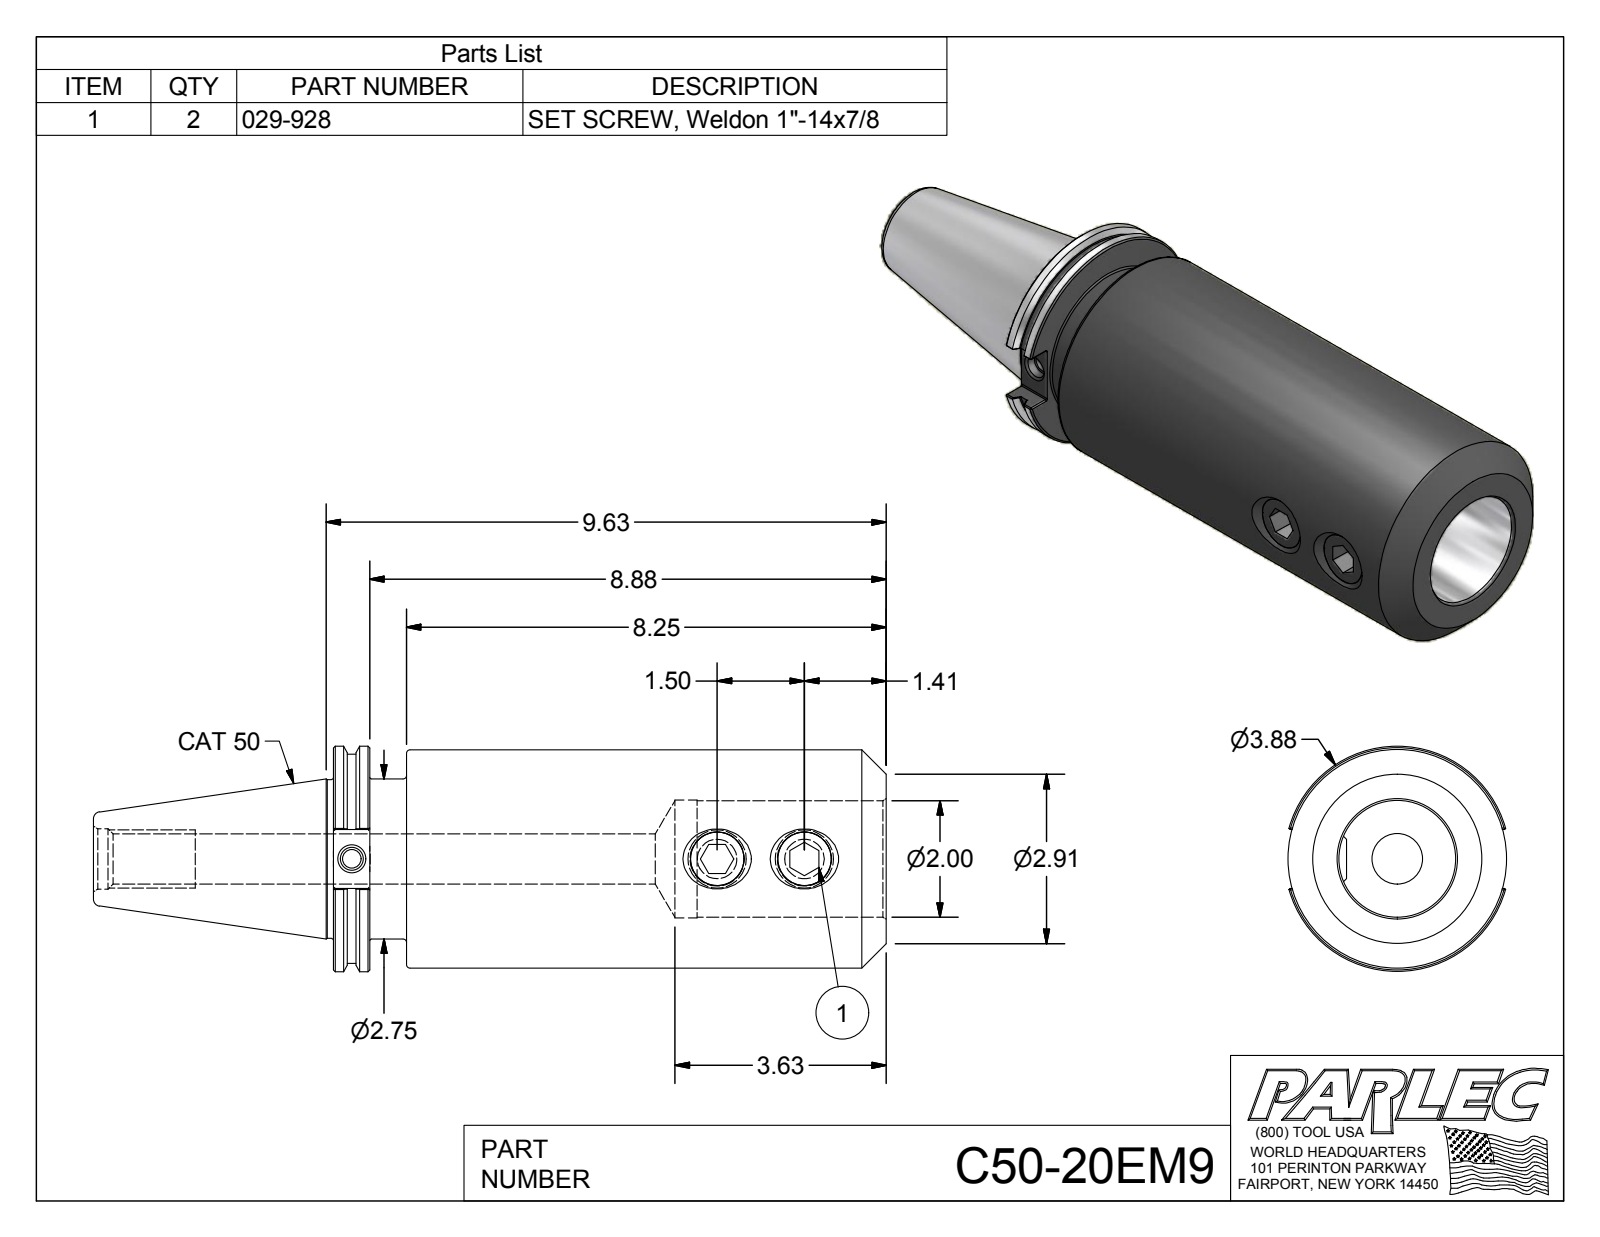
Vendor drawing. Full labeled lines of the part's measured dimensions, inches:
Part name (STEP PRODUCT): C50-20EM9; C50-20EM9-1; 029-928
STEP written by: Autodesk Inventor 2012 (AUTOMOTIVE_DESIGN)
Units: inches
Bodies: 3 solids, 119 faces (52 planar, 31 cylindrical, 36 other)
Overall size (bounding box): 13.625 × 3.875 × 3.75
Volume: 98.17 in³ · Surface area: 225.4 in²
Round holes (diameter × count): ⌀0.923 ×2, ⌀0.315 ×1, ⌀0.399 ×1, ⌀0.865 ×1, ⌀1.038 ×1, ⌀2 ×1, ⌀2.03 ×1
Round bosses / shafts (diameter × count): ⌀1 ×2, ⌀3.875 ×1, ⌀3.75 ×1, ⌀3.594 ×1, ⌀2.75 ×1, ⌀2.73 ×1
Partial cylindrical surfaces — rounded edges, fillets, slot ends (radius × count): R0.02 ×12
Main face-to-face distances: 0.625, 1.255, 0.63, 9.5, 8.875, 8.245, 0.5, 0.875, 2.263, 3.137
Hole centre spacings: 1.5, 6.279, 7.779
